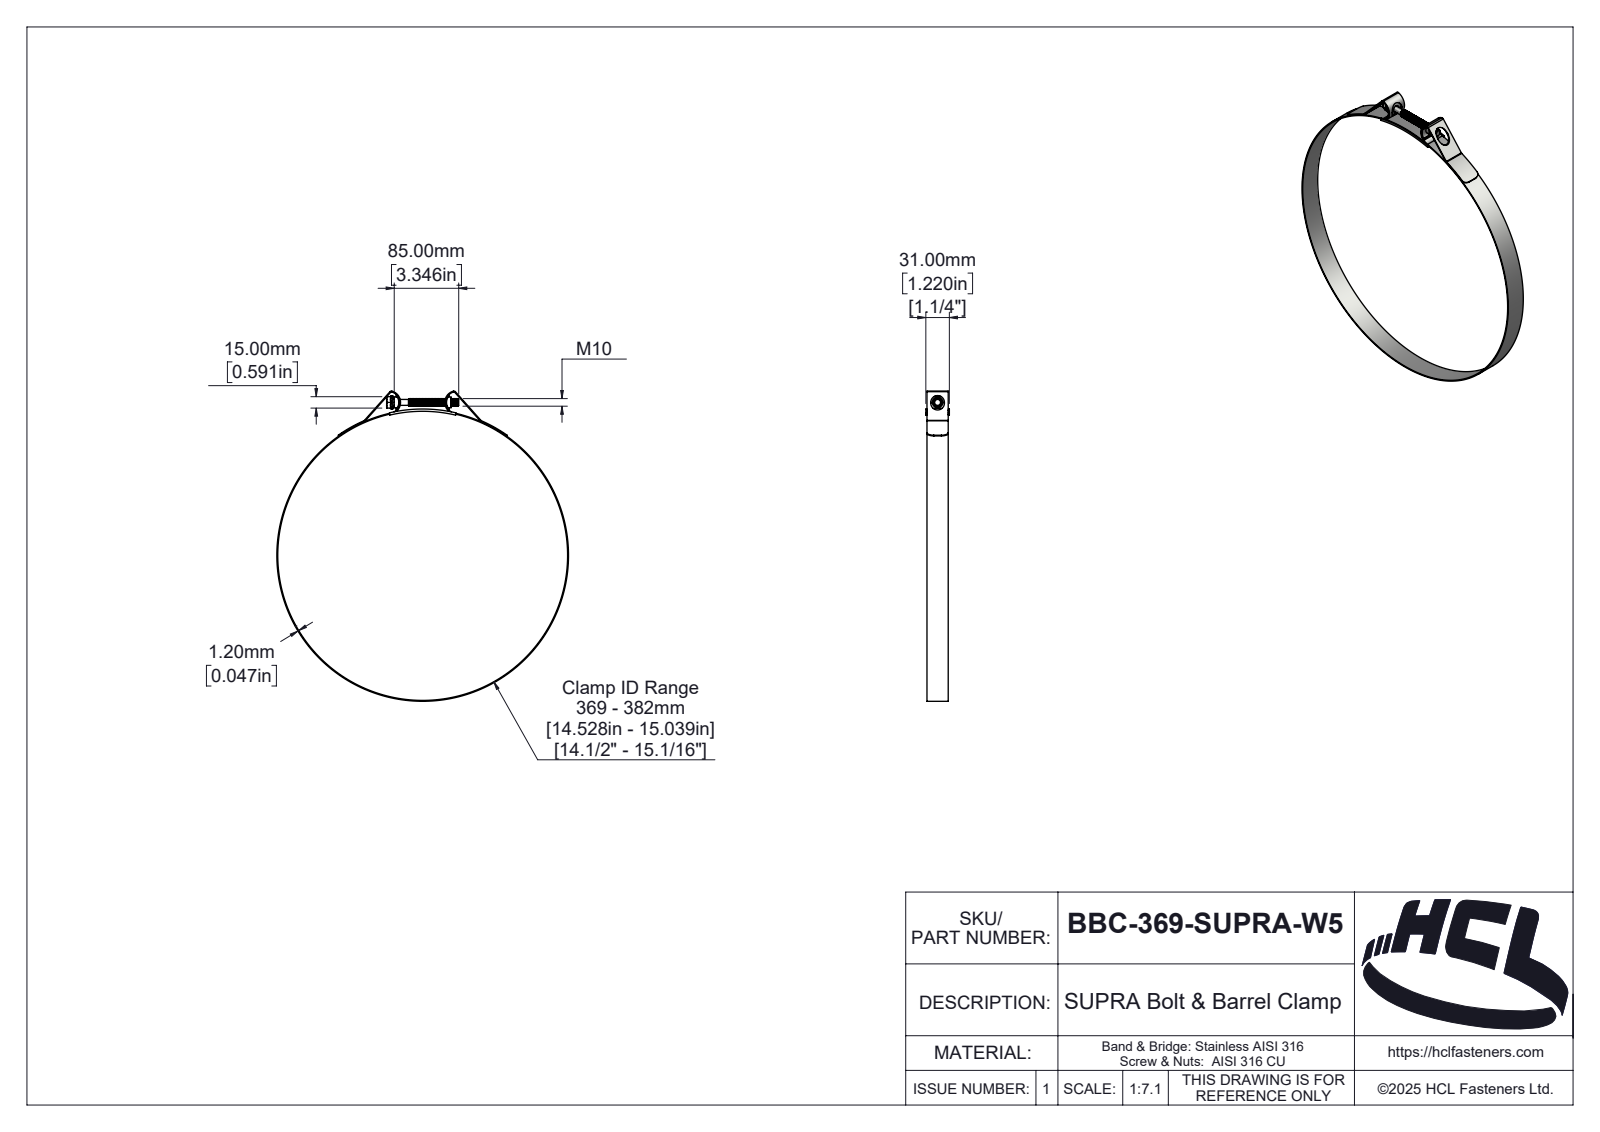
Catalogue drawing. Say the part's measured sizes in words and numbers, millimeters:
The part is named "BBC-369-SUPRA-W5". Its 3-D file was written by "SolidWorks 2025 (AUTOMOTIVE_DESIGN)". It is 5 solids with 377 faces: 50 planar, 241 cylindrical and 86 other. Overall it measures 408.66 by 384.4 by 31 millimeters. Its volume is 57 909 cubic millimeters and its surface area 92 627 square millimeters. Round holes: 1 of diameter 382. Round bosses or shafts: 1 of diameter 384.4, 1 of diameter 17.32, 1 of diameter 14, 1 of diameter 10, 1 of diameter 7.8. Partial cylindrical surfaces (rounded edges, fillets, slot ends): 4 of radius 1, 2 of radius 1.3, 2 of radius 2, 2 of radius 2.5, 2 of radius 3.2, 2 of radius 9, 2 of radius 13.08, 2 of radius 14.08. The main face-to-face distances are 1.2, 28, 1.5, 29.5, 29.8, 28.3, 31, 12.5, 82.5, 28.6.
